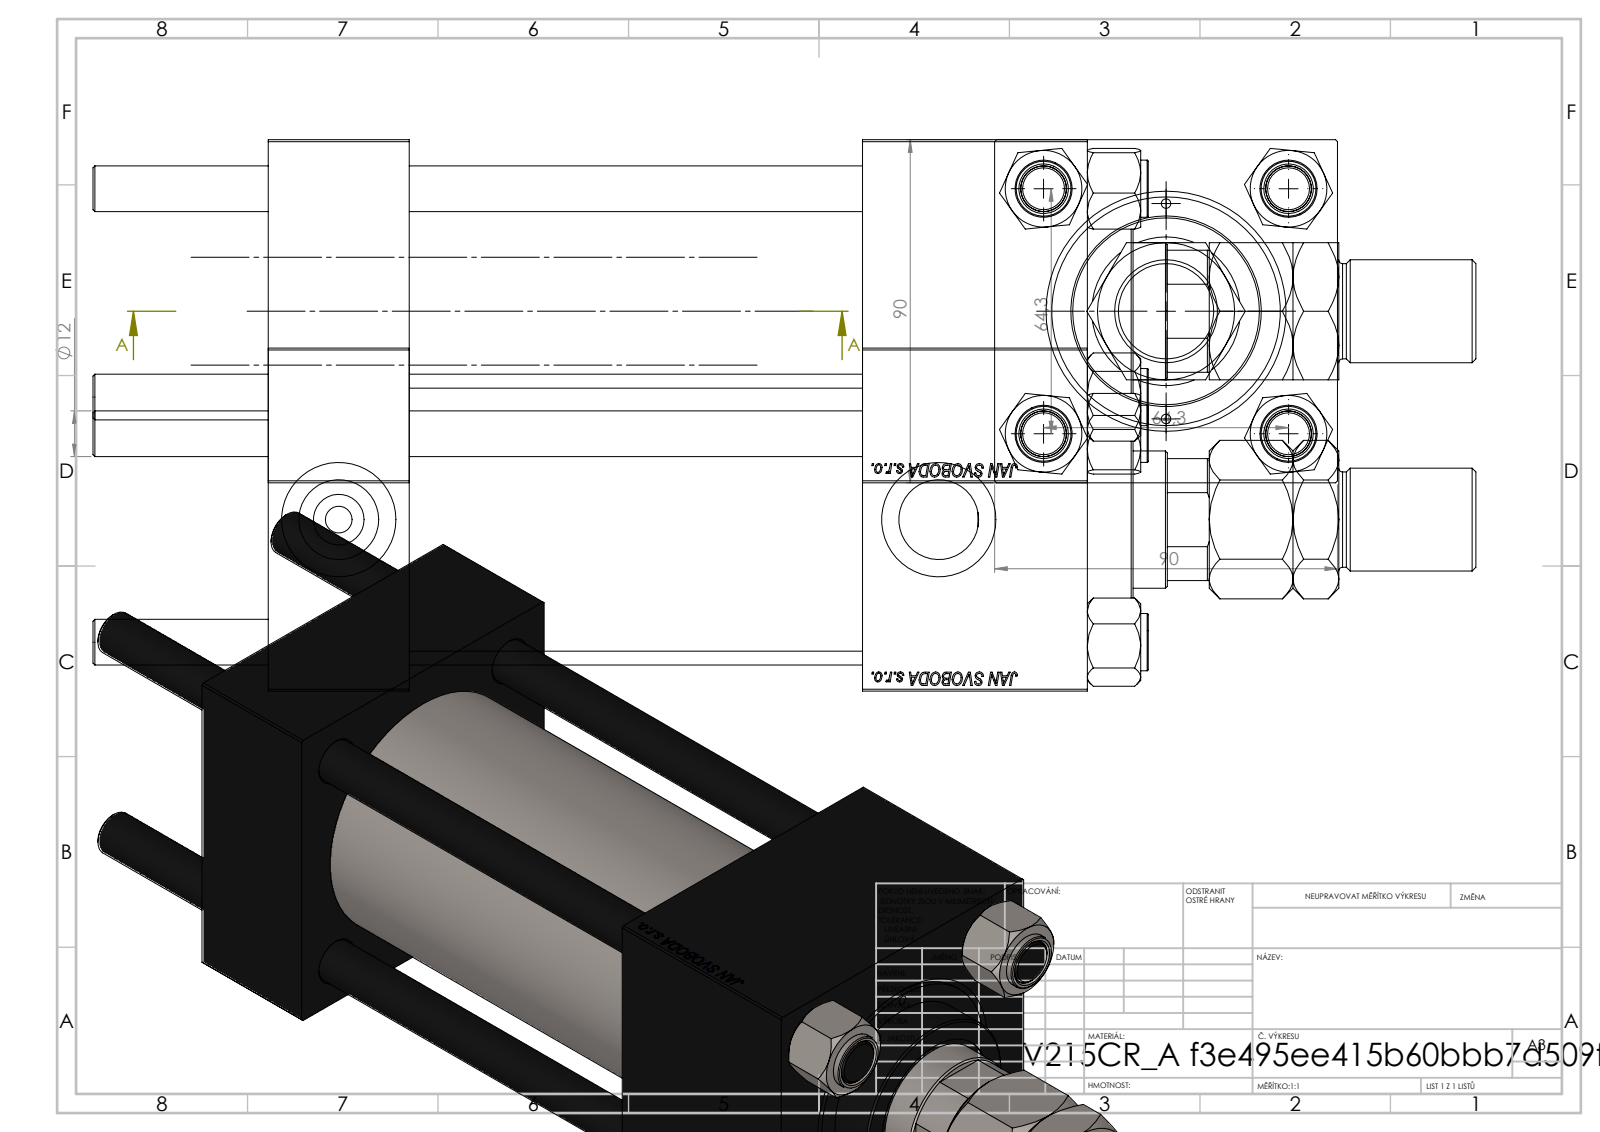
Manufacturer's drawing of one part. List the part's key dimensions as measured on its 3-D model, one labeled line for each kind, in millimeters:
Part name (STEP PRODUCT): NUT_M5; V215_VC_A; V215CR_BODY_A; CR025_012_A_0_G_A_G_M_020_+#_##_TYCINKA (+2 more)
STEP written by: SolidWorks 2019 (CONFIG_CONTROL_DESIGN)
Units: millimetres
Bodies: 12 solids, 1189 faces (537 planar, 86 cylindrical, 566 other)
Overall size (bounding box): 363 × 90 × 90
Volume: 1 186 000 mm³ · Surface area: 250 621 mm²
Round holes (diameter × count): ⌀12 ×4, ⌀2.5 ×2, ⌀7 ×2, ⌀20.96 ×2, ⌀30 ×2, ⌀25.5 ×1, ⌀36 ×1, ⌀39 ×1, ⌀50 ×1, ⌀60 ×1, ⌀63 ×1
Round bosses / shafts (diameter × count): ⌀15 ×4, ⌀69 ×1, ⌀27 ×1, ⌀25 ×1
Partial cylindrical surfaces — rounded edges, fillets, slot ends (radius × count): R17.5 ×1
Main face-to-face distances: 90, 37, 215, 178, 59, 156, 119, 186.3, 149.3, 30.3
Hole centre spacings: 32.39, 45.47, 64.3, 68.42, 28.25, 90.93, 56.5, 157.5
